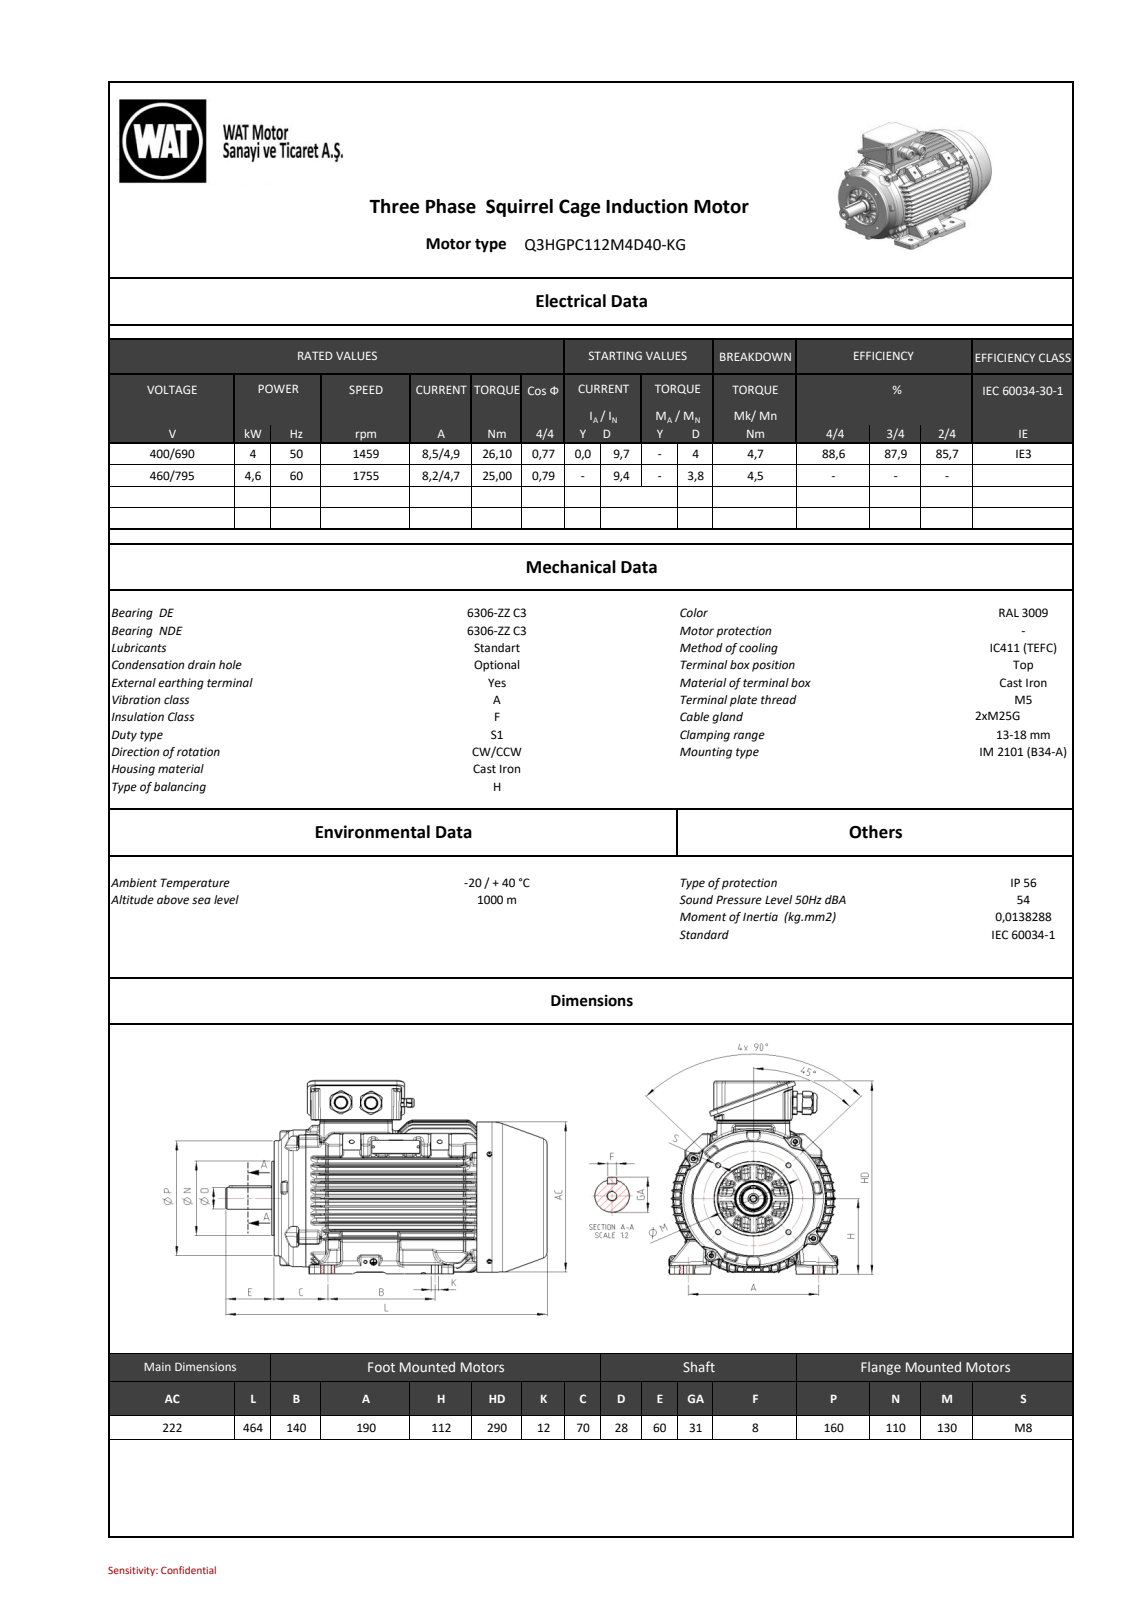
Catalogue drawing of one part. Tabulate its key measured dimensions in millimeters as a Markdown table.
| quantity | value |
| --- | --- |
| part name | 26000A30F4D8rp1a |
| STEP written by | SIEMENS PLM Software NX 11.0 (AUTOMOTIVE_DESIGN) |
| units | millimeters |
| bodies | 0 solids, 5622 faces (1046 planar, 1630 cylindrical, 2946 other) |
| overall size | 463.5 × 289.89 × 249 |
| round holes (diameter × count) | 5 × 9, 4.5 × 6, 3.5 × 5, 8.5 × 5, 3.3 × 3, 2.5 × 2, 6.8 × 2, 10 × 2, 17.2 × 2, 4 × 1, 8 × 1, 10.5 × 1 |
| round bosses / shafts (diameter × count) | 10 × 4, 27.7 × 2, 25.25 × 2, 20 × 2, 215 × 1, 192 × 1, 110 × 1, 35.83 × 1 |
| partial cylindrical surfaces (radius × count) | 4 × 284, 3 × 157, 0.5 × 132, 1.5 × 96, 2 × 64, 5 × 43, 1.8 × 40, 1 × 29 |
| main face-to-face distances | 13.1, 26.28, 13.18, 39.96, 90.54, 39.54, 26.44, 13.26, 77.36, 64.26 |
| hole center spacings | 115, 34.87, 97, 106.98, 125.79, 137.18, 161.41, 33.69 |
